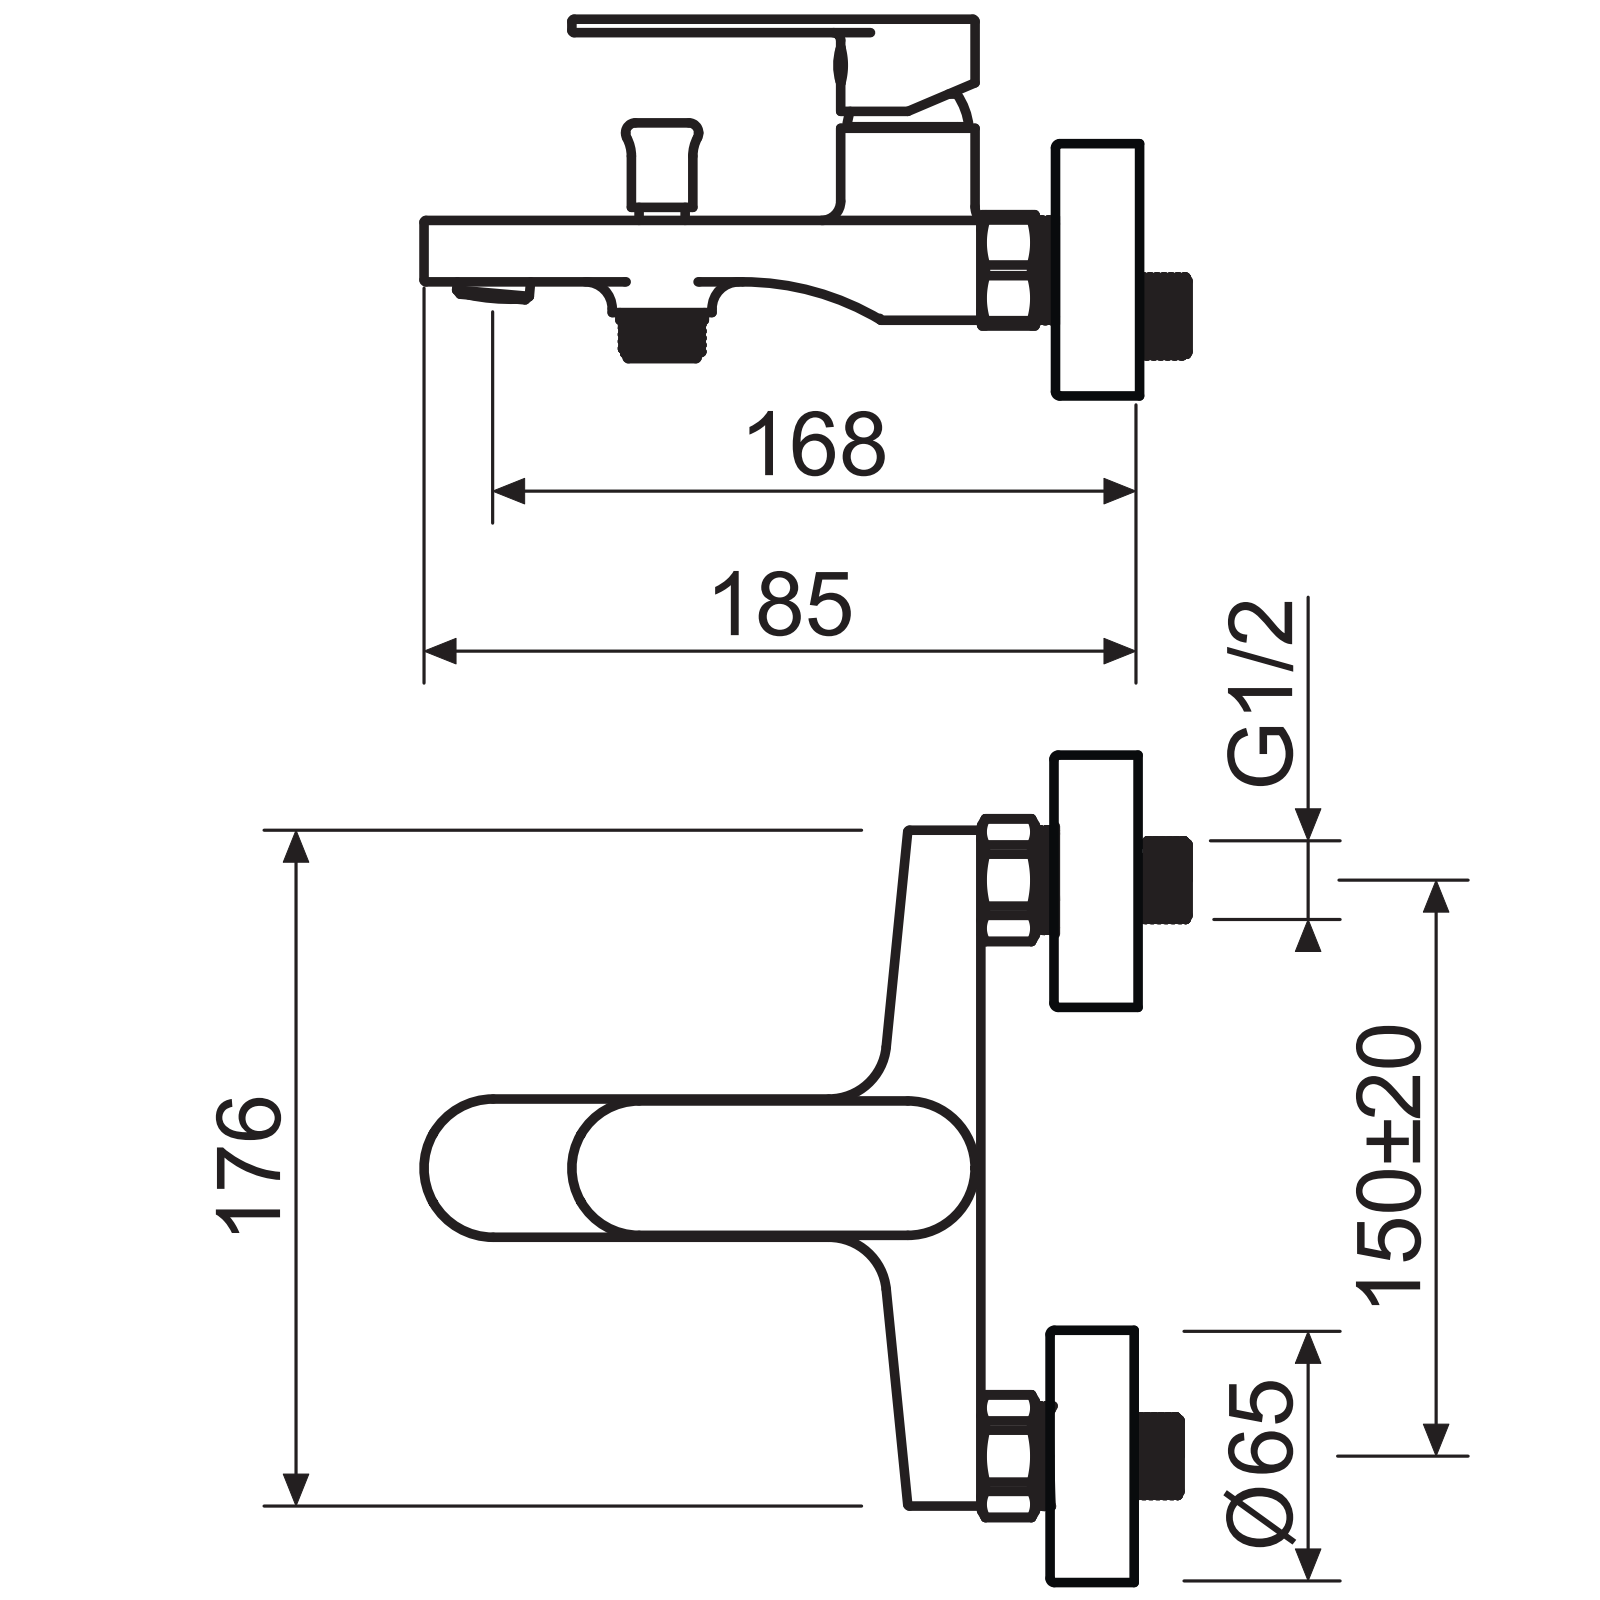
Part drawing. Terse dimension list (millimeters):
name: AUNO100C001; SARMAC0016; SCRPKC0250; SCRPKC0251 (+8 more)
written by: CREO PARAMETRIC BY PTC INC, 2022164 (CONFIG_CONTROL_DESIGN)
unit: mm
bodies: 44 solids, 7645 faces (3726 planar, 2189 cylindrical, 1730 other)
size: 833 × 314.9 × 97.6
volume: 979 900 mm³; area: 995 958 mm²
holes: 4× ⌀16, 3× ⌀3.3, 3× ⌀14.5, 3× ⌀19, 3× ⌀24.5, 3× ⌀25, 2× ⌀1, 2× ⌀1.3, 2× ⌀2, 2× ⌀2.5, 2× ⌀2.8, 2× ⌀4.2
bosses: 3× ⌀23, 3× ⌀18, 3× ⌀1, 2× ⌀65, 2× ⌀27.4, 2× ⌀26.4, 2× ⌀26.15, 2× ⌀24.3
rounds: 143× R0.2, 108× R0.3, 99× R0.5, 39× R1, 30× R0.6, 27× R1.5, 25× R0.3, 18× R0.1
face distances: 2, 58, 17.8, 8, 25.8, 40.2, 32.2, 60, 56, 10
hole spacings: 11.56, 8, 150, 0.5, 1.44, 3.39, 3.5, 4.16
